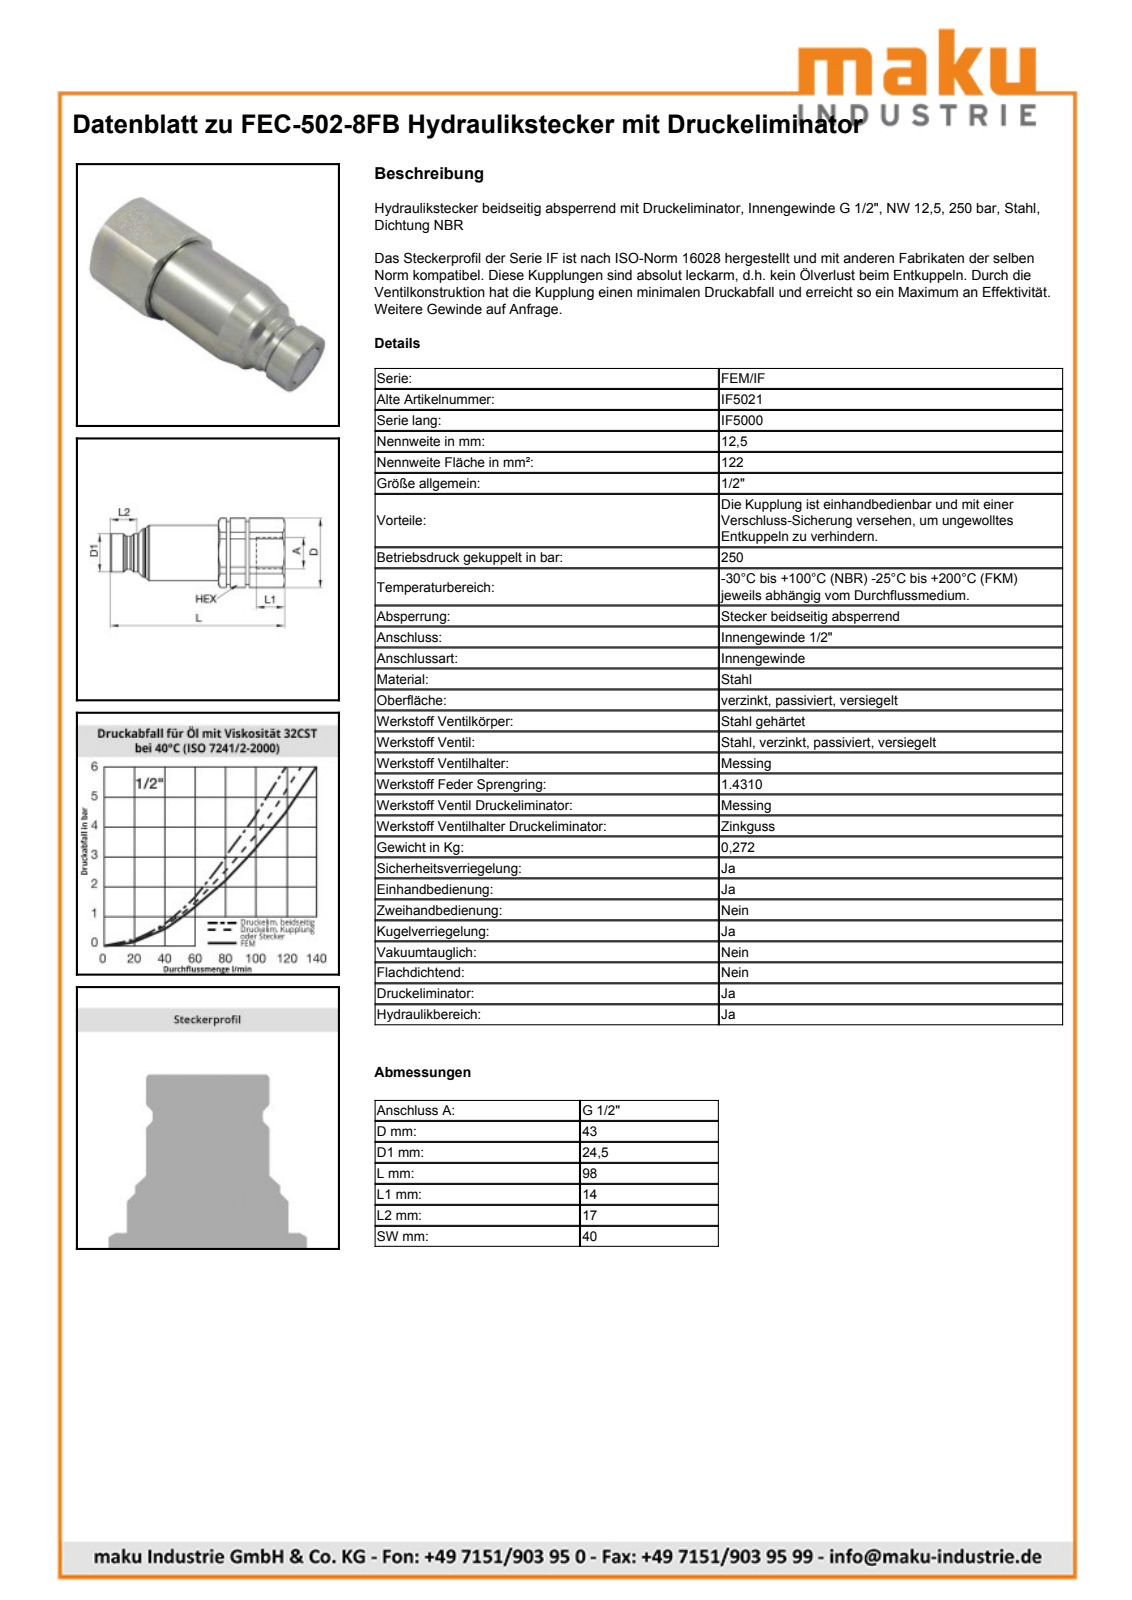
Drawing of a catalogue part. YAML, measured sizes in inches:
part_name: "FEC-502-8FB"
step_written_by: "SolidWorks 2009 (CONFIG_CONTROL_DESIGN)"
units: inches
bodies: {solids: 1, faces: 79, planar: 13, cylindrical: 20, other: 46}
overall_size: [3.843, 1.693, 1.575]
volume: 5.526
surface_area: 21.68
round_holes:
  - {diameter: 0.733, count: 1}
round_bosses_or_shafts:
  - {diameter: 1.378, count: 1}
  - {diameter: 1.368, count: 1}
  - {diameter: 1.201, count: 1}
  - {diameter: 0.965, count: 1}
  - {diameter: 0.866, count: 1}
partial_cylinders:
  - {radius: 0.846, count: 1}
face_to_face_distances: [1.575, 0.63, 1.26, 2.583, 3.213, 3.843, 2.58, 3.21, 3.84, 2.579]
